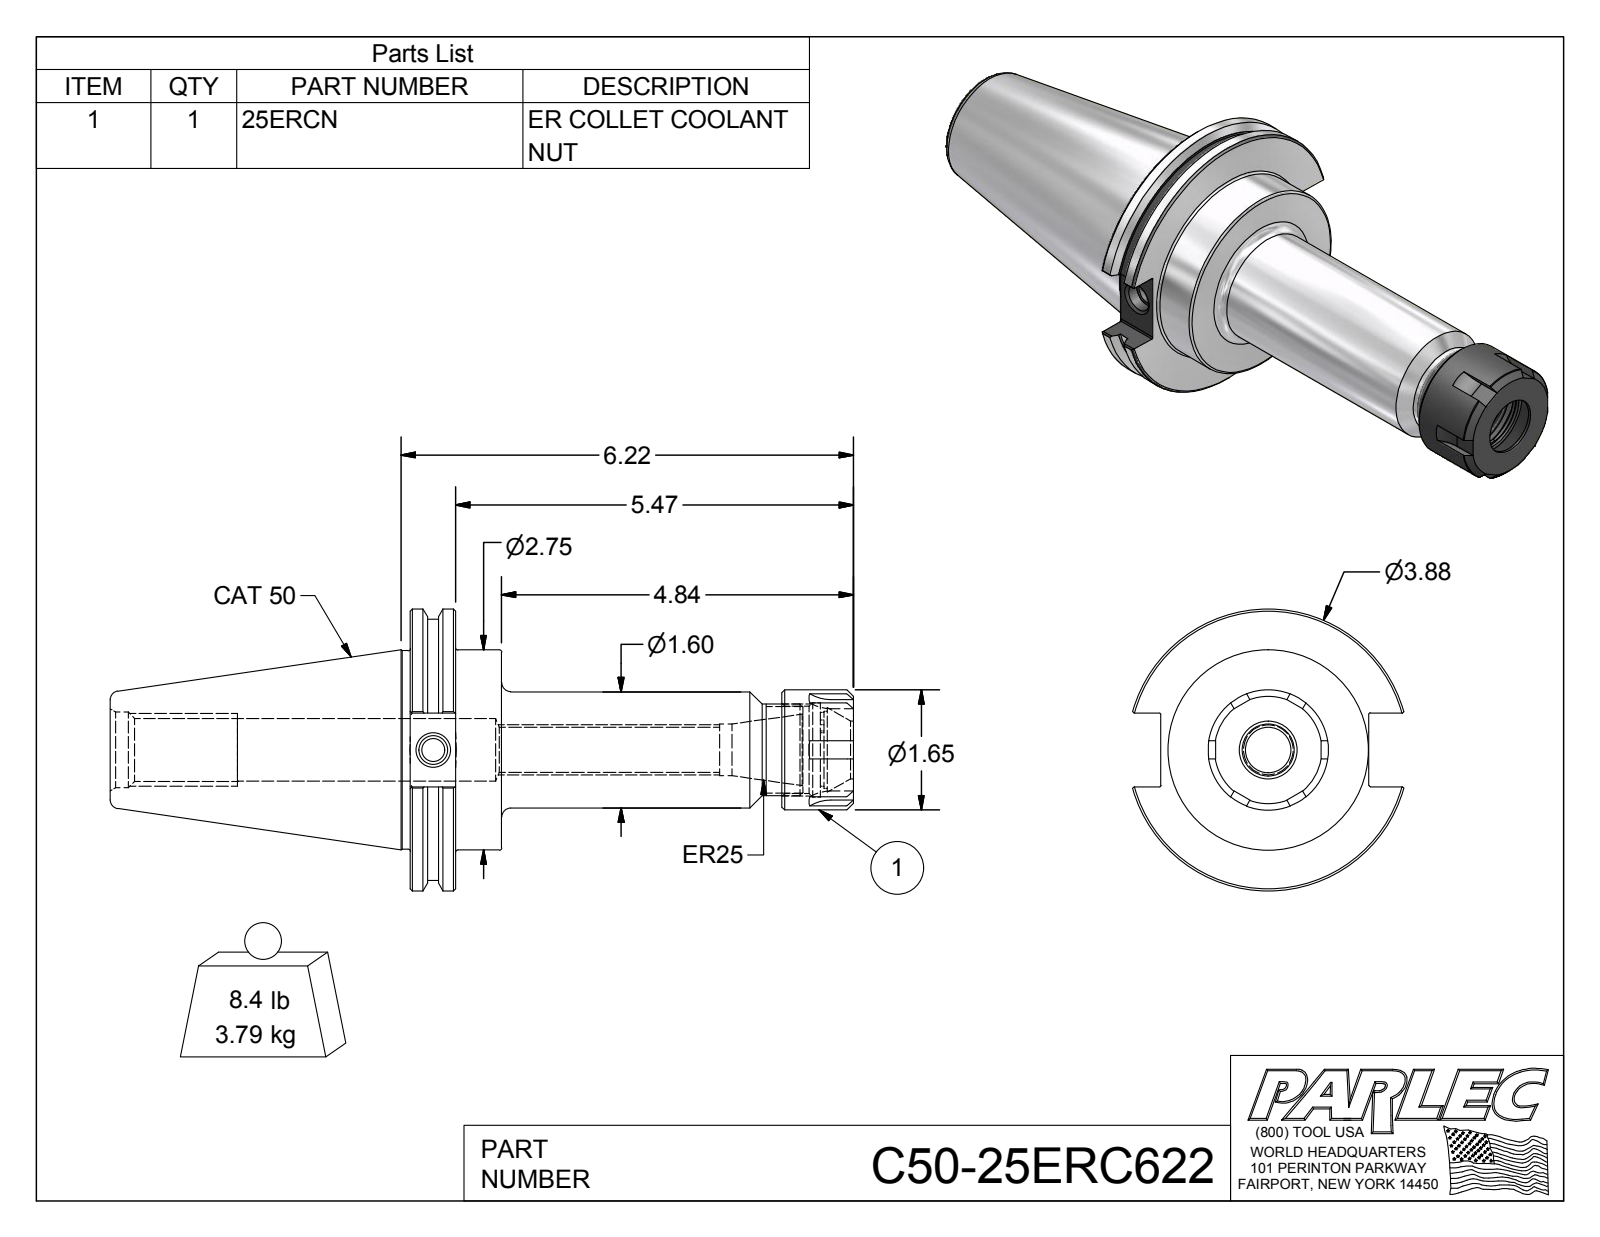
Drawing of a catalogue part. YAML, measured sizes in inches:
part_name: "C50-25ERC622; C50-25ER6-1; 25ERCN"
step_written_by: "Autodesk Inventor 2012 (AUTOMOTIVE_DESIGN)"
units: inches
bodies: {solids: 2, faces: 139, planar: 57, cylindrical: 41, other: 41}
overall_size: [10.22, 3.875, 3.729]
volume: 30.09
surface_area: 115.3
round_holes:
  - {diameter: 0.315, count: 1}
  - {diameter: 0.399, count: 1}
  - {diameter: 0.62, count: 1}
  - {diameter: 0.71, count: 1}
  - {diameter: 0.794, count: 1}
  - {diameter: 0.864, count: 1}
  - {diameter: 0.865, count: 1}
  - {diameter: 1.038, count: 1}
  - {diameter: 1.057, count: 1}
  - {diameter: 1.201, count: 1}
  - {diameter: 1.294, count: 1}
round_bosses_or_shafts:
  - {diameter: 3.875, count: 1}
  - {diameter: 3.594, count: 1}
  - {diameter: 2.75, count: 1}
  - {diameter: 2.73, count: 1}
  - {diameter: 1.654, count: 1}
  - {diameter: 1.595, count: 1}
  - {diameter: 1.26, count: 1}
partial_cylinders:
  - {radius: 0.02, count: 8}
  - {radius: 0.5, count: 6}
  - {radius: 0.472, count: 1}
  - {radius: 0.515, count: 1}
face_to_face_distances: [0.625, 1.255, 0.63, 6.095, 5.47, 4.84, 5.111, 4.486, 3.856, 0.984]
